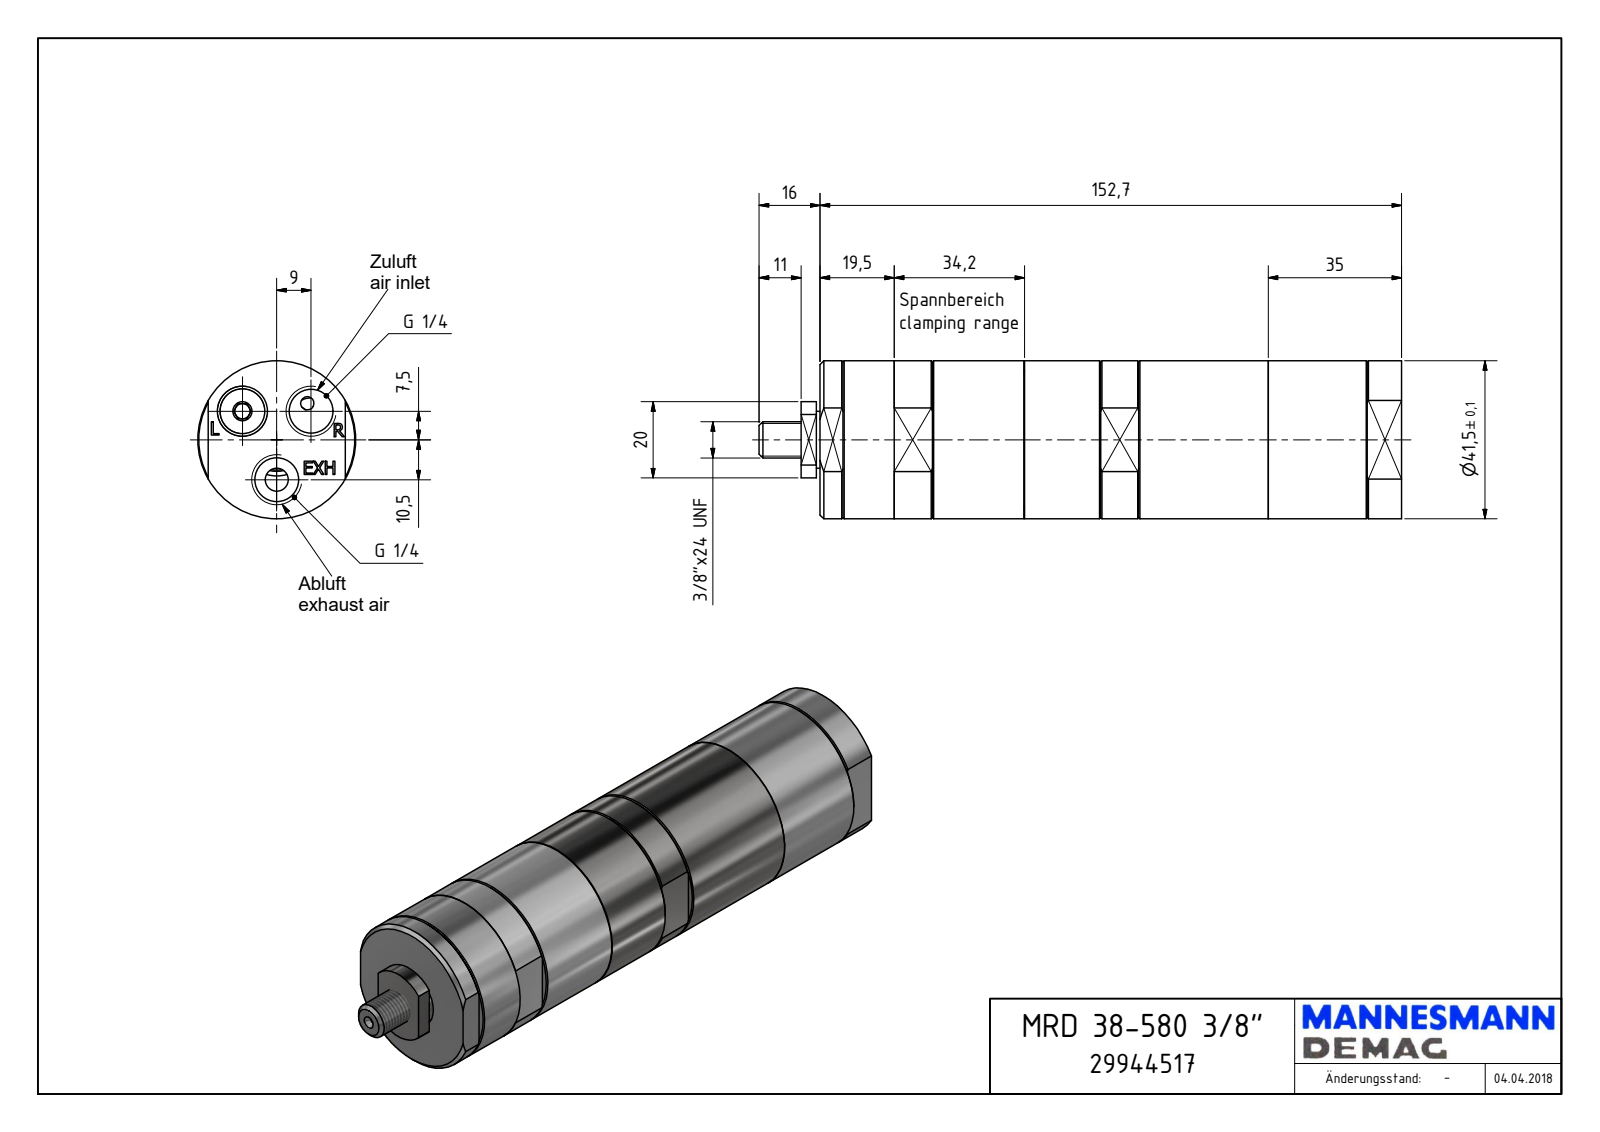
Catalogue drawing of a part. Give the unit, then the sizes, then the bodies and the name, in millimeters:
Units: millimetres
Overall size (bounding box): 168.7 × 41.5 × 41.5
Round holes (diameter × count): ⌀11.45 ×3, ⌀1.6 ×1, ⌀4 ×1, ⌀16 ×1
Round bosses / shafts (diameter × count): ⌀41.5 ×1, ⌀36 ×1, ⌀14.95 ×1, ⌀9.53 ×1
Partial cylindrical surfaces — rounded edges, fillets, slot ends (radius × count): R10 ×1
Main face-to-face distances: 152.7, 1, 38, 37, 53.7, 99, 53.5, 99.2, 142.07, 88.57
Hole centre spacings: 11.72, 20.12, 10.5, 18
Volume: 204 274 mm³ · Surface area: 25 363 mm²
Bodies: 1 solid, 163 faces (106 planar, 24 cylindrical, 33 other)
Part name (STEP PRODUCT): MRD 38-580 3-8_29944517
STEP written by: Autodesk Inventor 2018 (AUTOMOTIVE_DESIGN)
